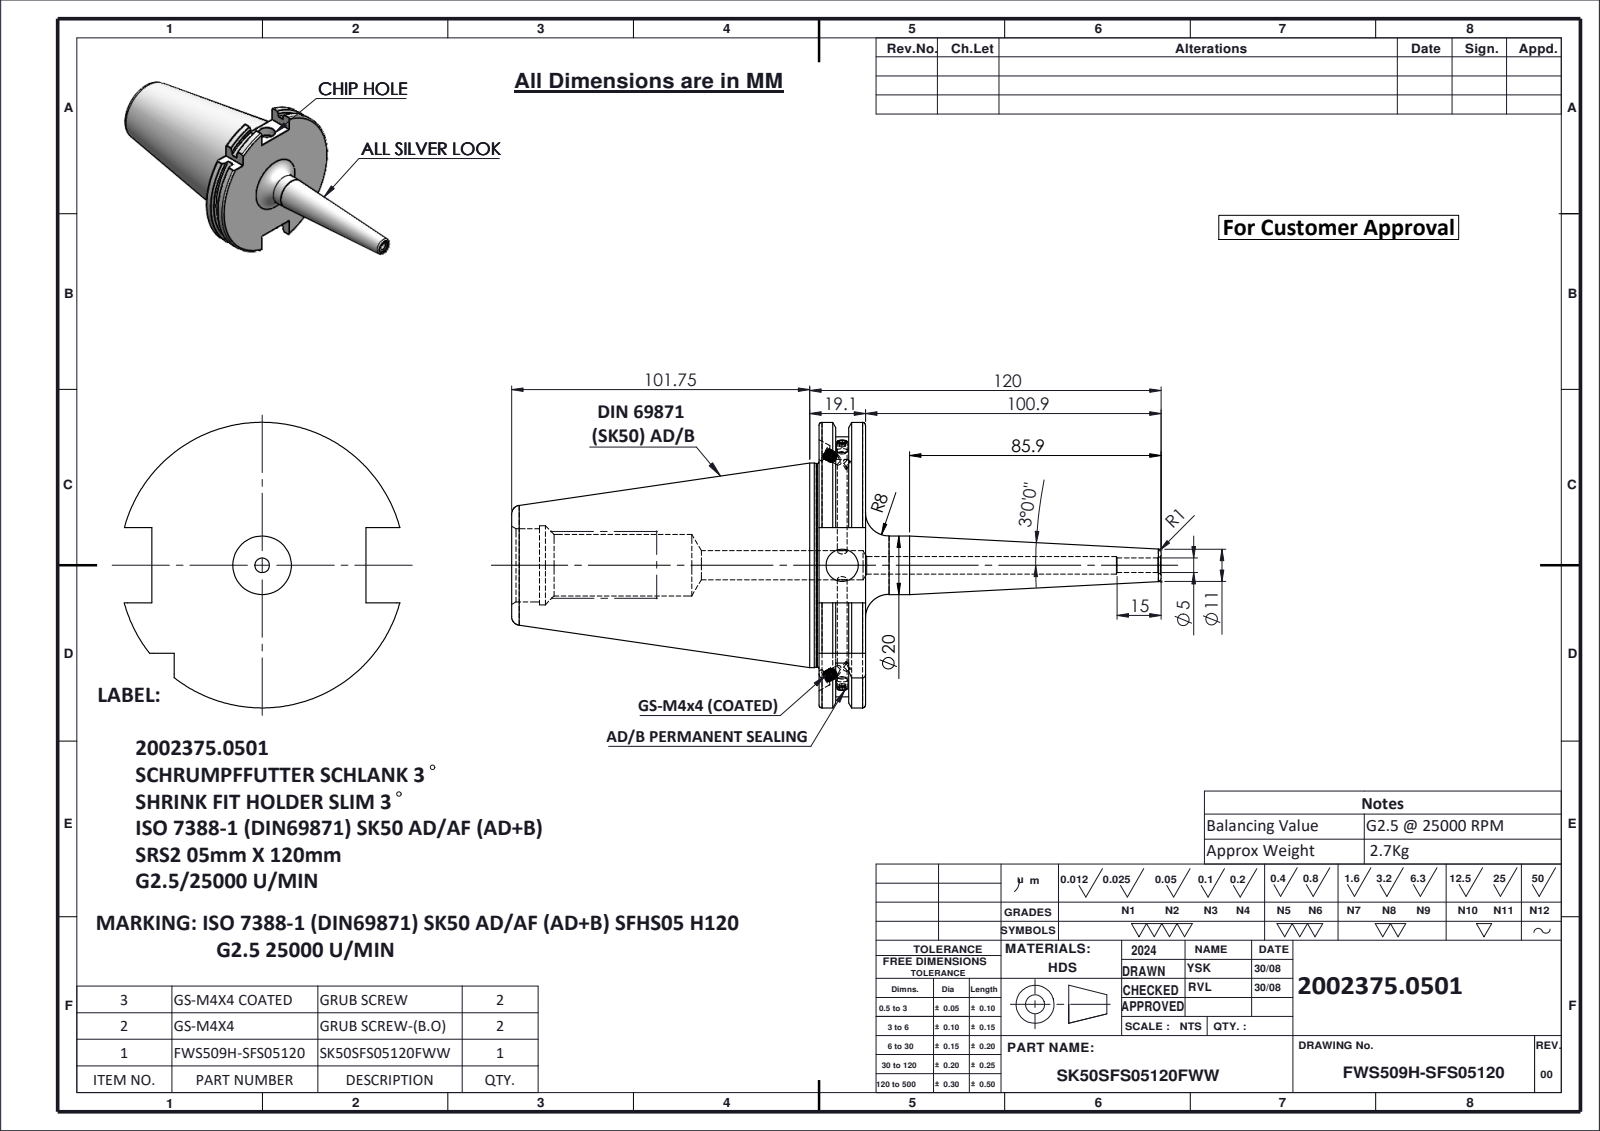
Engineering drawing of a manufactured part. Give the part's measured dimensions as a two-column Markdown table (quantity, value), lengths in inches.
| quantity | value |
| --- | --- |
| part name | SK50SFS05120FWW; FWS509H-SFS05120; GS-M4X4-COATING_DIN 913 - M4 x 4-N; GS-M4X4_DIN 913 - M4 x 4-N |
| STEP written by | SolidWorks 2024 (CONFIG_CONTROL_DESIGN) |
| units | inches |
| bodies | 5 solids, 254 faces (61 planar, 75 cylindrical, 118 other) |
| overall size | 8.73 × 3.839 × 3.703 |
| volume | 21.55 in³ |
| surface area | 77.97 in² |
| round holes (diameter × count) | 0.236 × 3, 0.126 × 2, 0.13 × 1, 0.197 × 1, 0.394 × 1, 0.433 × 1, 0.827 × 1, 0.984 × 1, 1.063 × 1 |
| round bosses / shafts (diameter × count) | 0.157 × 4, 0.114 × 2, 2.75 × 1, 2.734 × 1, 0.787 × 1 |
| partial cylindrical surfaces (radius × count) | 1.768 × 1, 1.919 × 1 |
| main face-to-face distances | 0.626, 0.222, 0.404, 0.399, 0.177, 0.227, 4.132, 4.354, 4.531, 4.758 |
